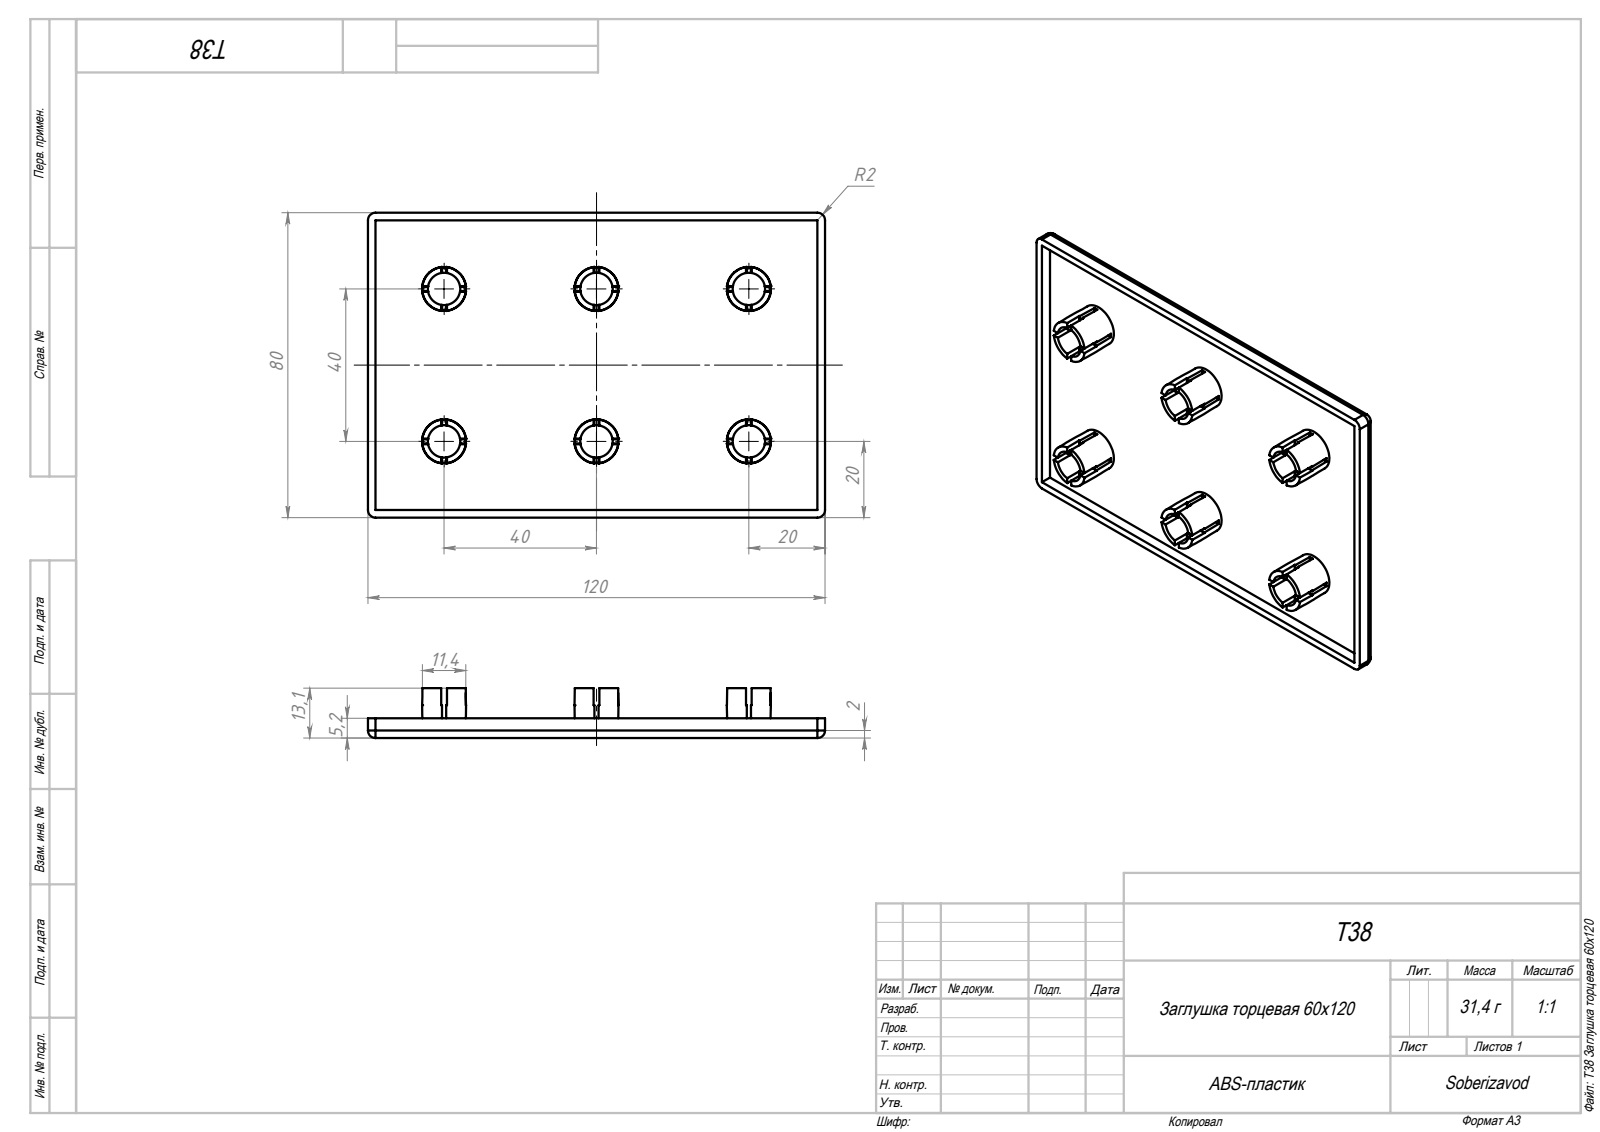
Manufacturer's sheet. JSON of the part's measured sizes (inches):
{"part_name": "T38 Заглушка торцевая 60x120", "step_written_by": "SolidWorks 2018 (AUTOMOTIVE_DESIGN)", "units": "inches", "bodies": {"solids": 7, "faces": 245, "planar": 209, "cylindrical": 20, "other": 16}, "overall_size": [4.724, 3.15, 0.516], "volume_in3": 1.571, "surface_area_in2": 41.6, "round_holes": [[0.335, 6]], "partial_cylinders_radius": [[0.079, 8]], "face_to_face_distances": [0.087, 0.079, 0.205, 0.118, 3.071, 3.15, 4.646, 1.575, 2.992, 0.051], "hole_center_spacings": [1.575, 2.227, 3.15, 3.521]}
